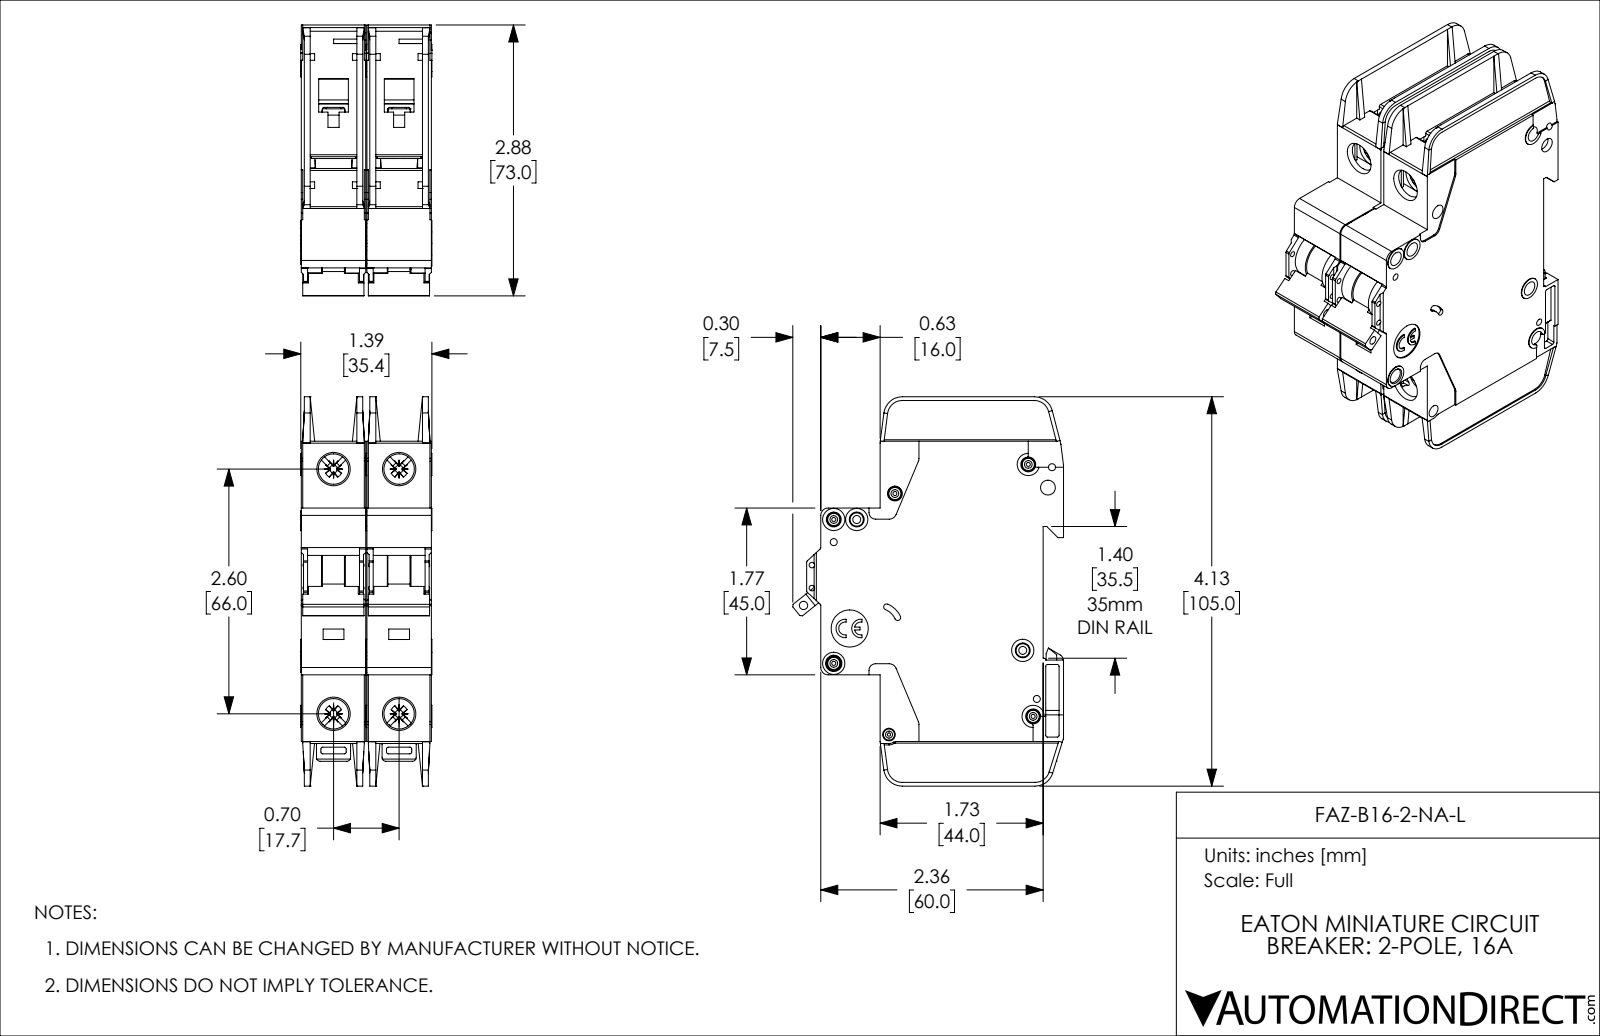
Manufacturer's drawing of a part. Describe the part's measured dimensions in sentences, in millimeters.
The part is named "FAZ-B16-2-NA-L". Its 3-D file was written by "SolidWorks 2019 (AUTOMOTIVE_DESIGN)". It is 2 solids with 2254 faces: 1342 planar, 714 cylindrical and 198 other. Overall it measures 105 by 73.1 by 35.4 millimeters. Its volume is 153 500 cubic millimeters and its surface area 52 910 square millimeters. Round holes: 8 of diameter 4, 5 of diameter 1.1, 4 of diameter 1.9, 4 of diameter 8.2, 2 of diameter 1.5, 2 of diameter 2.2, 1 of diameter 0.9, 1 of diameter 2.3, 1 of diameter 2.5, 1 of diameter 3.4, 1 of diameter 10. Round bosses or shafts: 5 of diameter 3.3, 4 of diameter 6, 3 of diameter 3, 2 of diameter 2.5. Partial cylindrical surfaces (rounded edges, fillets, slot ends): 57 of radius 0.5, 20 of radius 0.4, 14 of radius 1, 10 of radius 2, 8 of radius 1.1, 5 of radius 0.2, 5 of radius 5, 4 of radius 0.3. The main face-to-face distances are 17.7, 1.2, 17.4, 15, 2.4, 16.2, 13.8, 35.1, 18.9, 16.5. The hole center spacings are 6.2, 13.6, 17.7, 22.1, 66, 68.3, 4.8, 5.1.
